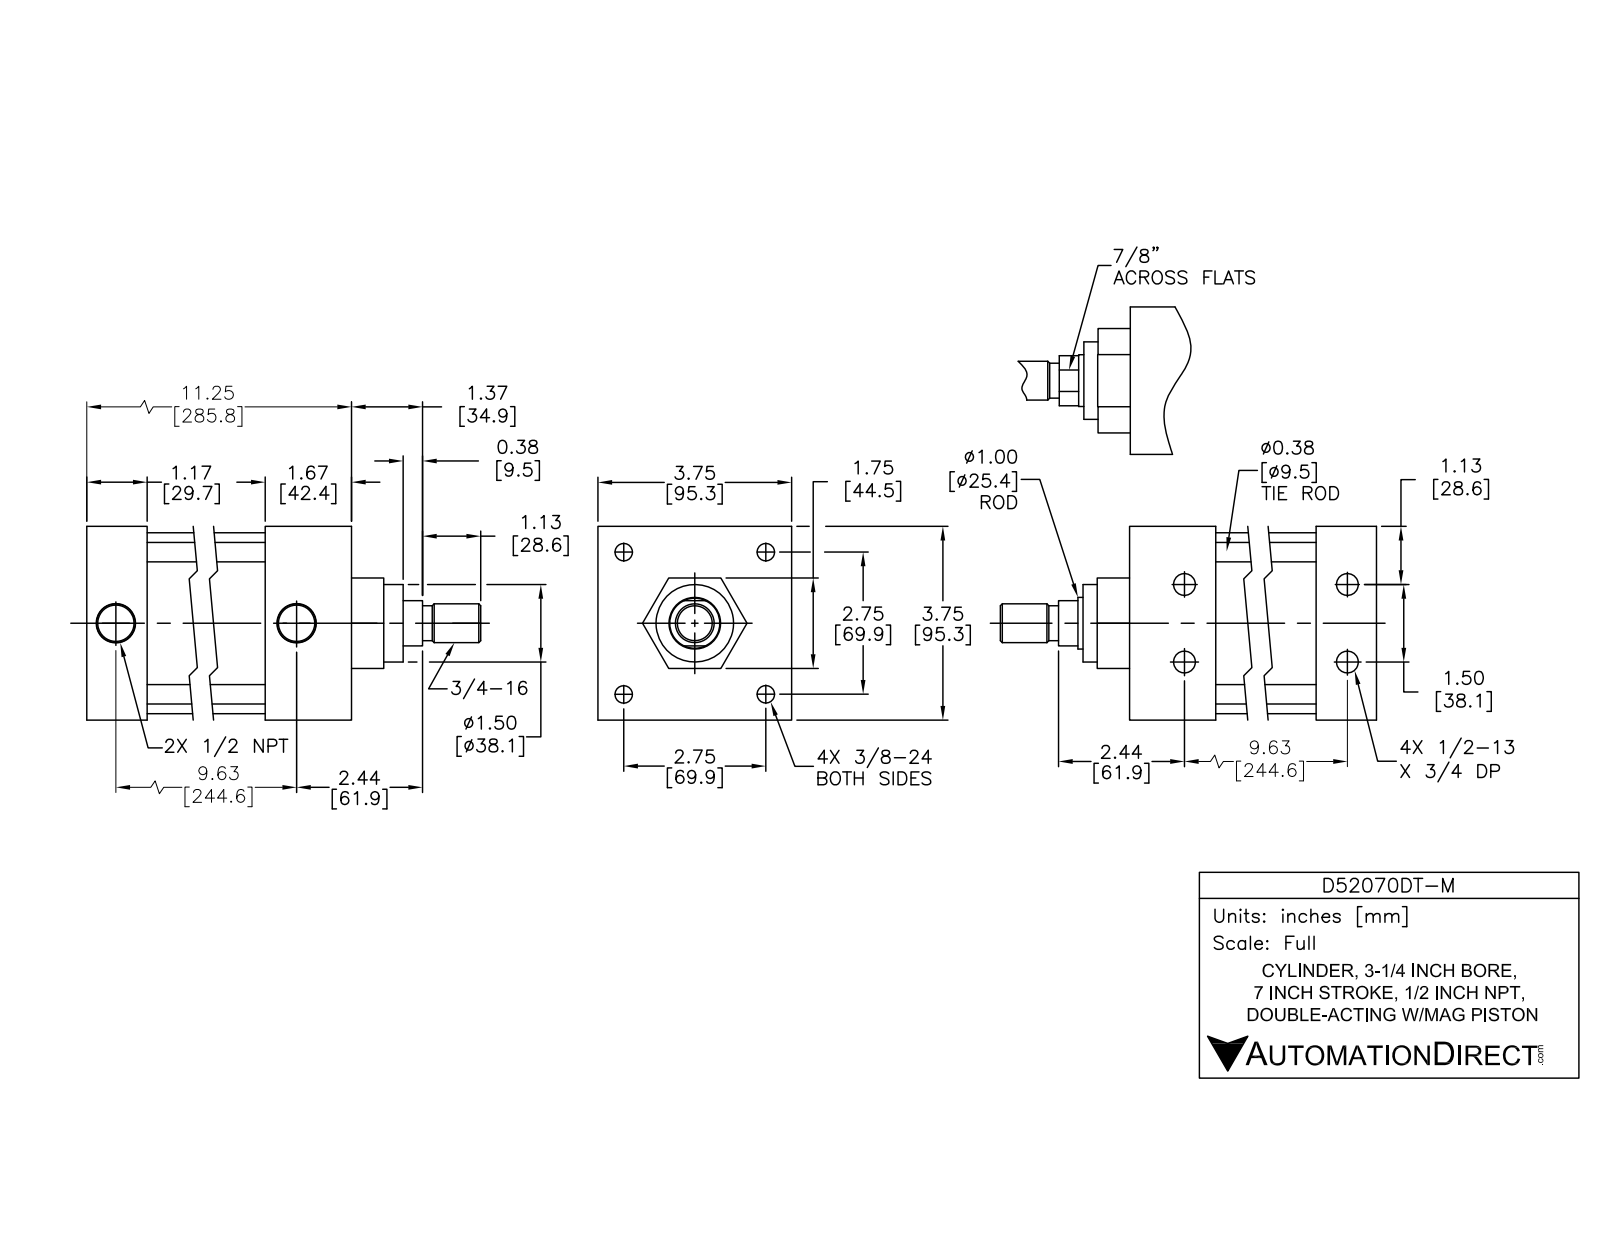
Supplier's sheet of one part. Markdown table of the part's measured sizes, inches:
| quantity | value |
| --- | --- |
| part name | D52070DT-M PISTON; D52070DT-M; D52070DT-M BODY |
| STEP written by | SolidWorks 2015 (AUTOMOTIVE_DESIGN) |
| units | inches |
| bodies | 12 solids, 303 faces (99 planar, 114 cylindrical, 90 other) |
| overall size | 13.745 × 3.75 × 3.75 |
| volume | 71.11 in³ |
| surface area | 437.4 in² |
| round holes (diameter × count) | 0.33 × 4, 0.406 × 4, 0.417 × 4, 0.625 × 4, 0.5 × 2, 0.766 × 2, 1 × 1, 1.003 × 1, 3.25 × 1 |
| round bosses / shafts (diameter × count) | 0.609 × 4, 0.375 × 4, 0.34 × 4, 3.5 × 1, 3.247 × 1, 1.75 × 1, 0.997 × 1, 0.97 × 1 |
| partial cylindrical surfaces (radius × count) | 0.375 × 4 |
| main face-to-face distances | 3.75, 0.08, 8.326, 11.246, 1.75, 9.997, 1.249, 8.751, 1.246, 2.495 |
| hole center spacings | 0.75, 0.76, 1.5, 1.95, 1.95, 2.758, 2.758, 3.9 |
